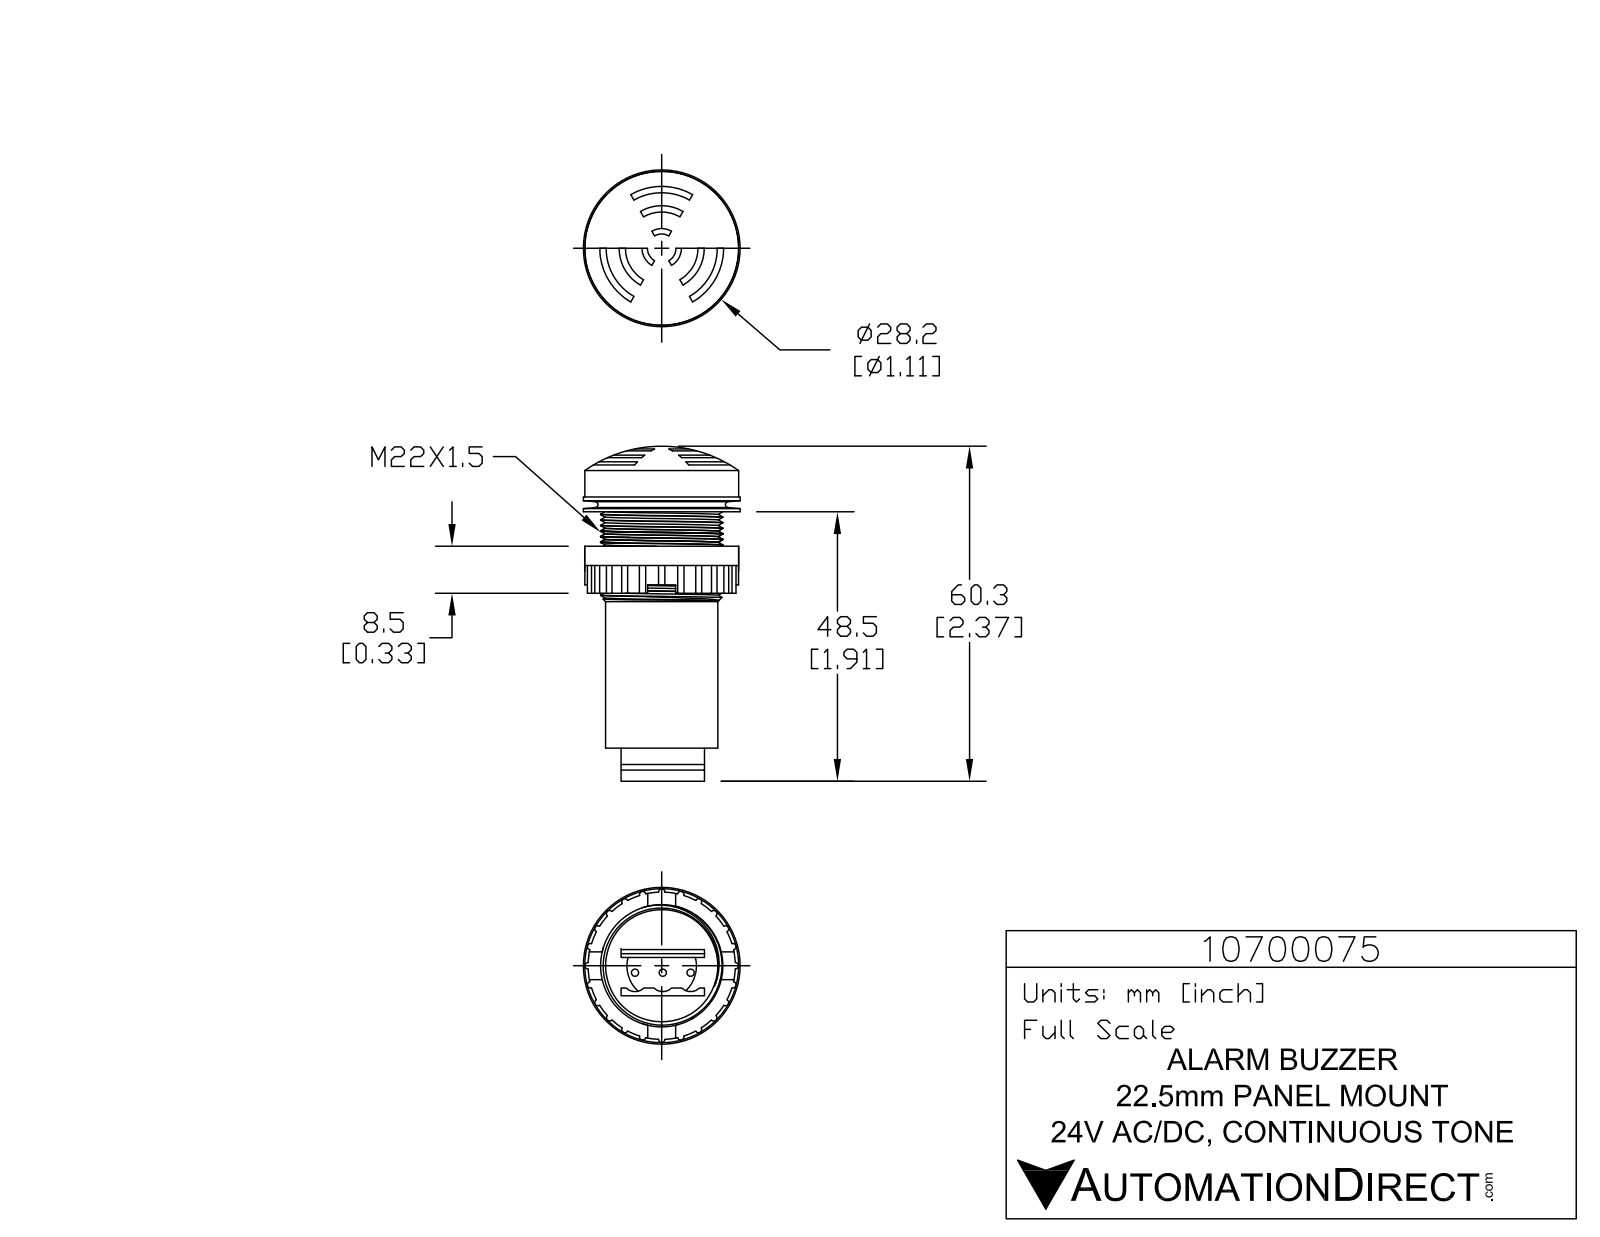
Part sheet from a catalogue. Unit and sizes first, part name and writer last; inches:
Units: inches
Overall size (bounding box): 2.339 × 1.11 × 1.11
Round bosses / shafts (diameter × count): ⌀0.051 ×3, ⌀1.11 ×1, ⌀1.091 ×1, ⌀0.866 ×1, ⌀0.795 ×1
Partial cylindrical surfaces — rounded edges, fillets, slot ends (radius × count): R0.022 ×24, R0.089 ×3, R0.246 ×1, R0.522 ×1
Main face-to-face distances: 1.398, 0.335, 1.063, 0.272, 1.297, 0.138, 1.64, 0.577, 0.242, 0.1
Volume: 1.317 in³ · Surface area: 12.29 in²
Bodies: 1 solid, 161 faces (37 planar, 103 cylindrical, 21 other)
Part name (STEP PRODUCT): 10700075
STEP written by: SolidWorks 2017 (AUTOMOTIVE_DESIGN)
